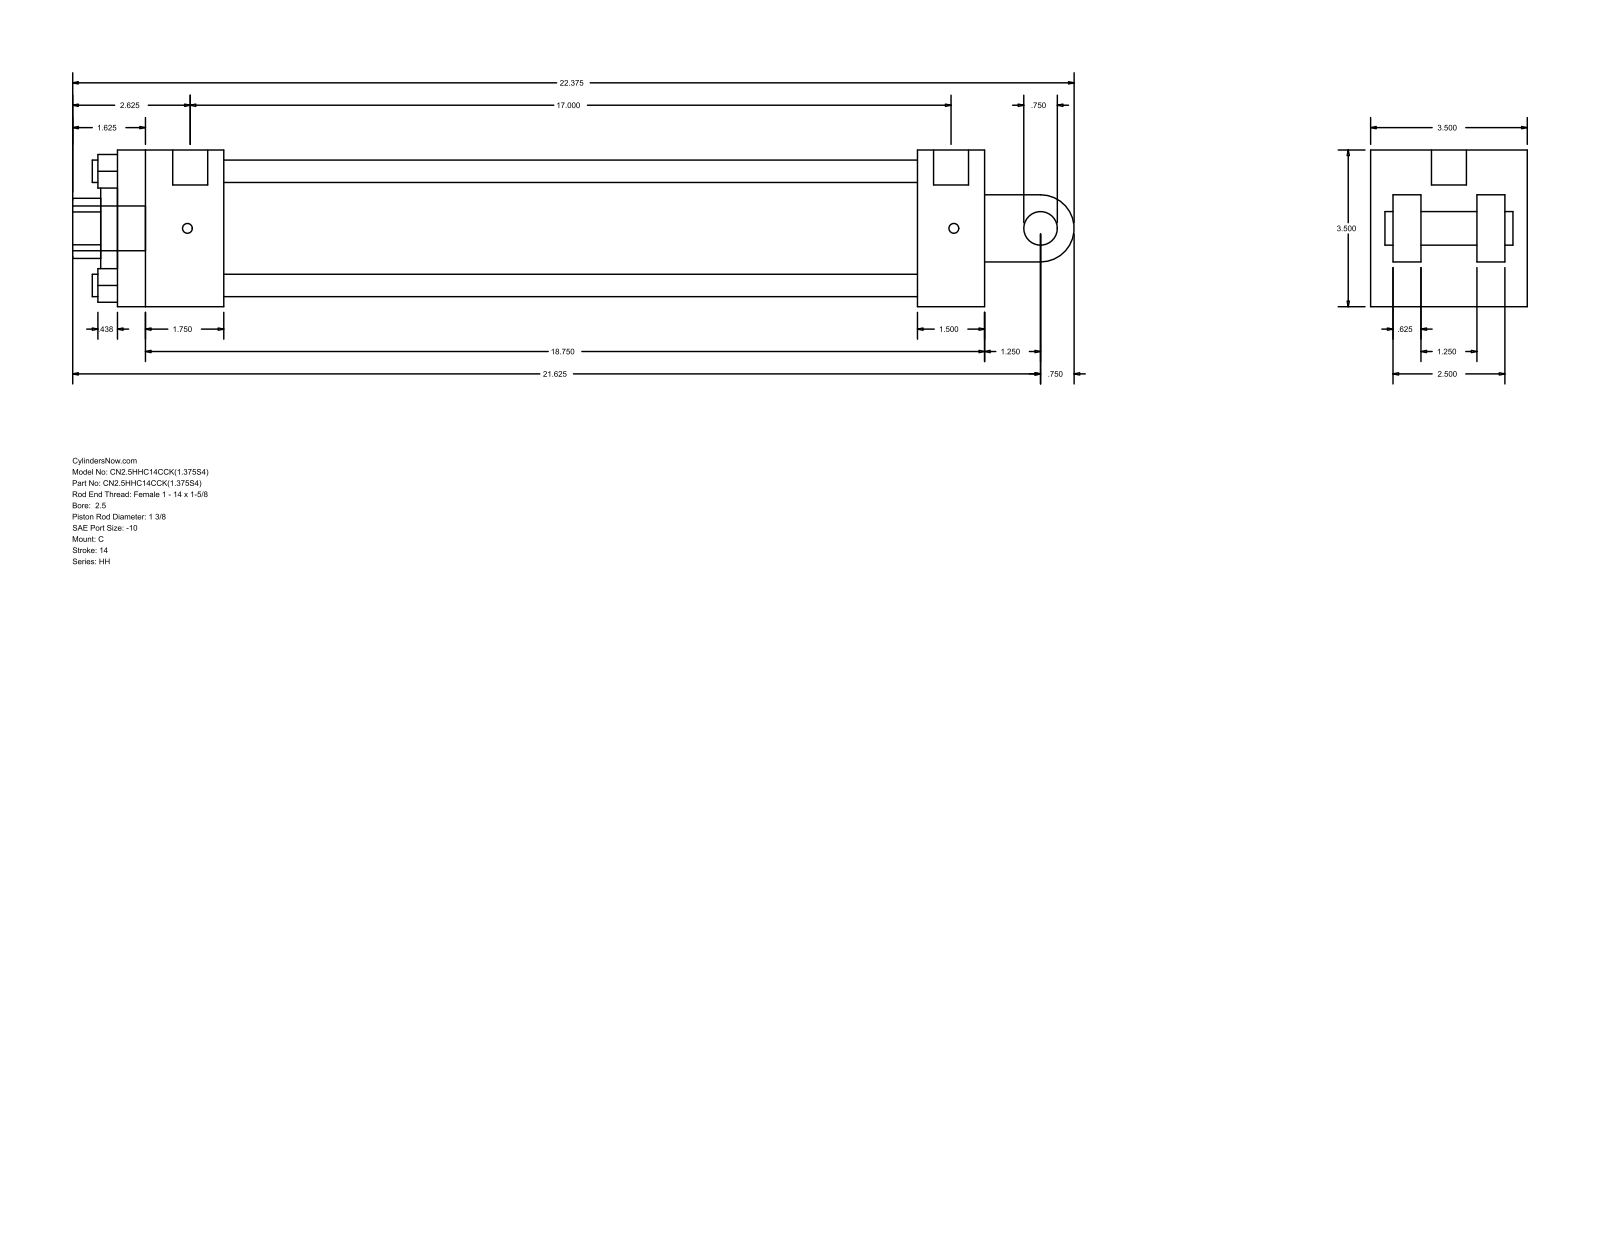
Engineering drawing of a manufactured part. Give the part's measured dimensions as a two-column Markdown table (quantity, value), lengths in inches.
| quantity | value |
| --- | --- |
| part name | HH_C__0250_1.375 |
| STEP written by | GSSL Pune (CONFIG_CONTROL_DESIGN) |
| units | inches |
| bodies | 0 solids, 99 faces (70 planar, 29 cylindrical, 0 other) |
| overall size | 22.375 × 3.5 × 3.5 |
| round holes (diameter × count) | 0.5 × 4, 0.219 × 2, 0.781 × 1, 1.375 × 1, 2 × 1, 2.875 × 1 |
| round bosses / shafts (diameter × count) | 0.219 × 2, 1 × 1, 0.781 × 1, 0.75 × 1 |
| partial cylindrical surfaces (radius × count) | 0.672 × 1, 0.75 × 1 |
| main face-to-face distances | 3.5, 19.375, 2.5, 0.625, 0.5, 17.875, 1.5, 2.375, 15.5, 17 |
| hole center spacings | 1.803, 2.55, 3.606, 0.062 |
